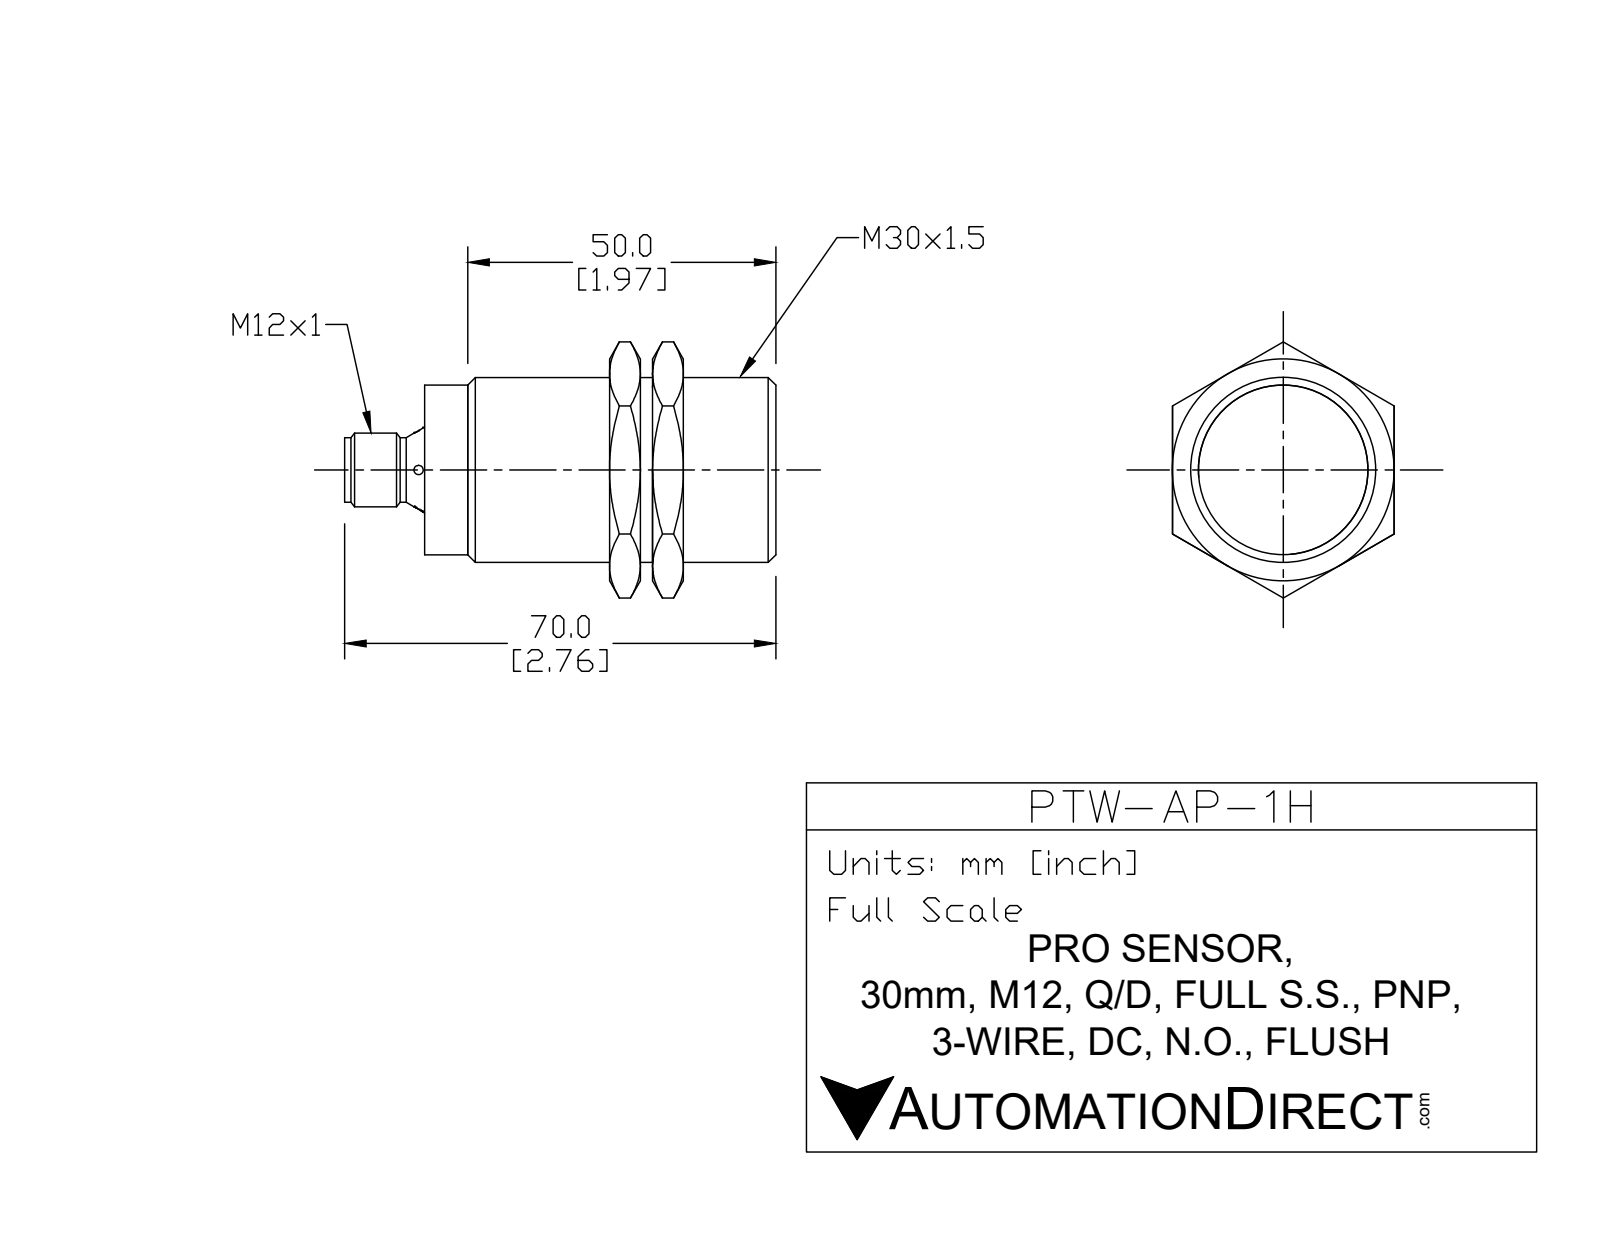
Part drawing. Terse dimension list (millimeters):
name: PTW-AP-1H
written by: SolidWorks 2017 (AUTOMOTIVE_DESIGN)
unit: mm
bodies: 3 solids, 97 faces (20 planar, 31 cylindrical, 46 other)
size: 70 × 41.6 × 36
volume: 45 030 mm³; area: 11 100 mm²
holes: 2× ⌀1.5, 1× ⌀9, 1× ⌀27.5, 1× ⌀28.4
bosses: 1× ⌀30, 1× ⌀12, 1× ⌀10.5
rounds: 1× R5.8
face distances: 5, 25, 36, 32, 57, 37, 20, 27, 10, 30
